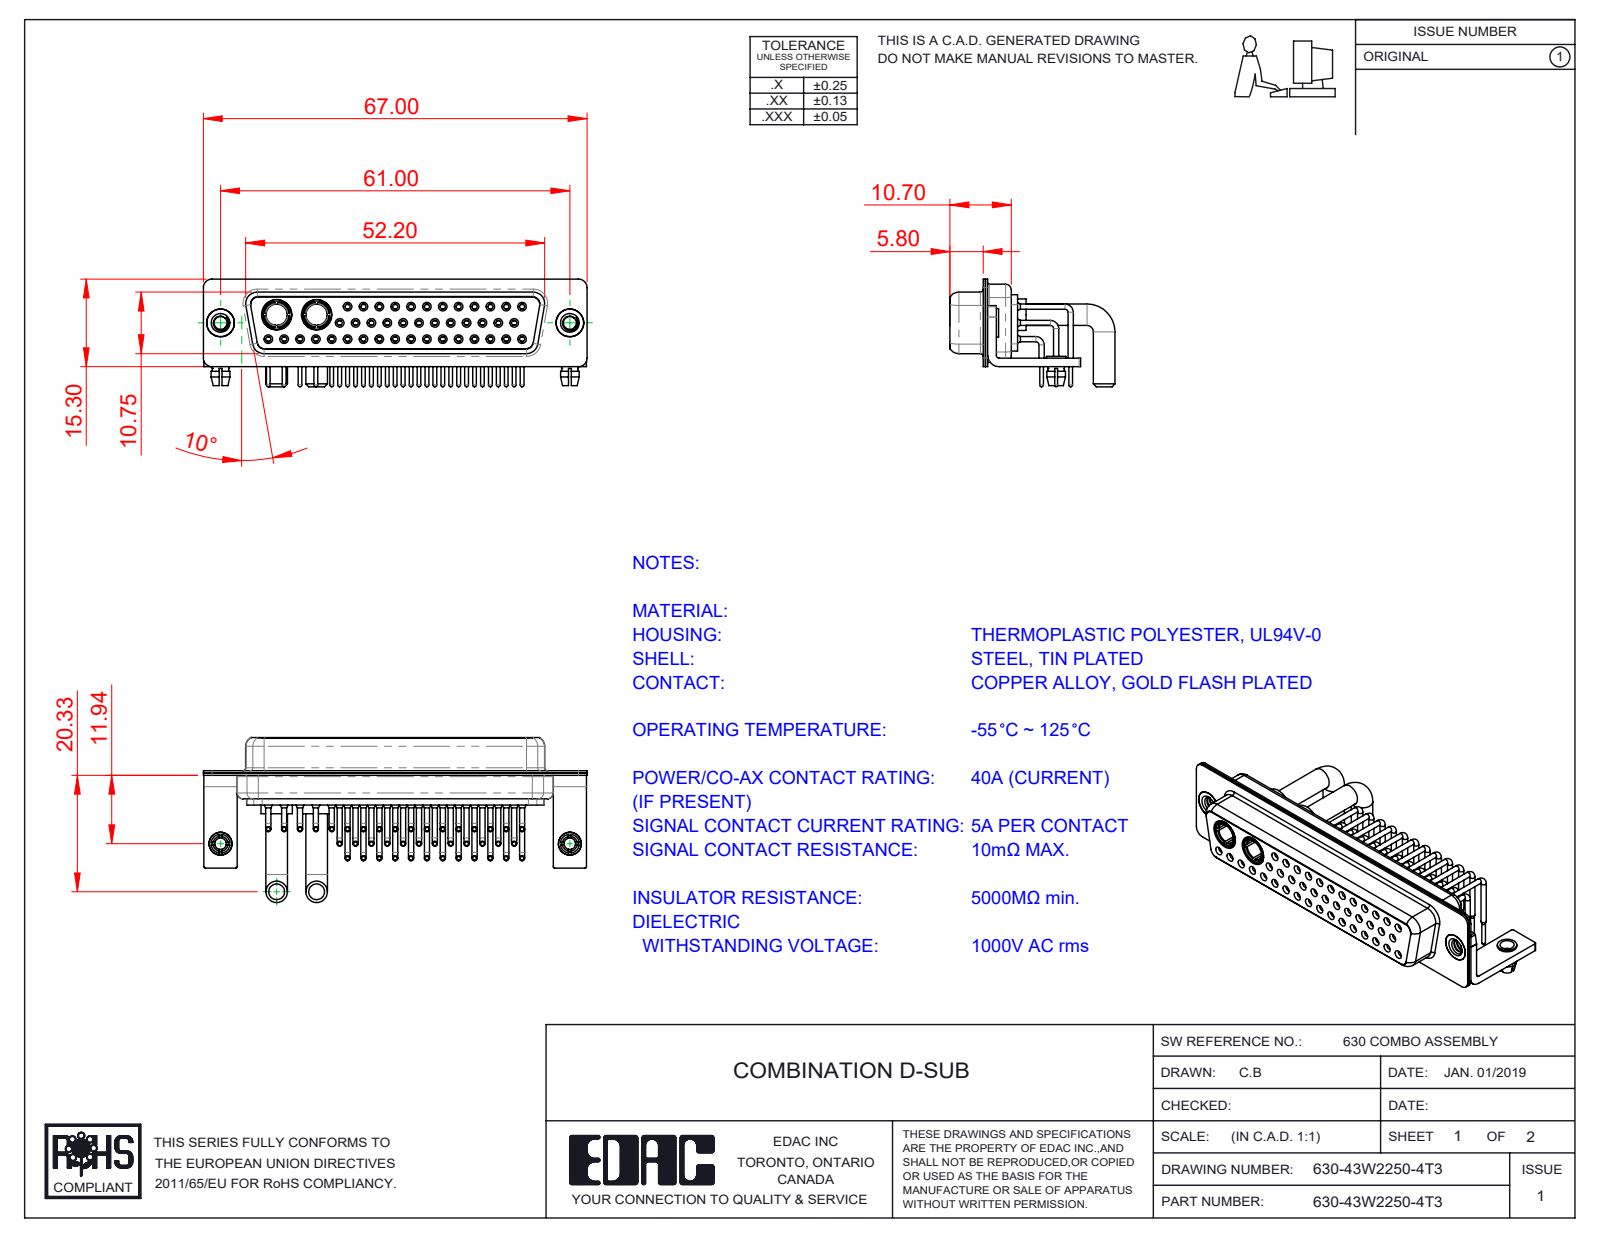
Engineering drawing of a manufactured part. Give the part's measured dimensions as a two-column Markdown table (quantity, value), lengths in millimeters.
| quantity | value |
| --- | --- |
| part name | 630Combo Shell Front_50 Contacts; Power Socket_Ext 40A RA 50; 630Combo Contact Row 2_50 Contacts; 630Combo Contact Row 3 (+7 more) |
| STEP written by | SolidWorks 2020 (CONFIG_CONTROL_DESIGN) |
| units | millimeters |
| bodies | 54 solids, 2740 faces (808 planar, 1180 cylindrical, 752 other) |
| overall size | 67 × 28.8 × 18.8 |
| volume | 7 934 mm³ |
| surface area | 17 047 mm² |
| round holes (diameter × count) | 2 × 43, 0.9 × 41, 1.1 × 41, 1.5 × 41, 1.6 × 29, 1.7 × 12, 4.85 × 4, 2.26 × 2, 2.5 × 2, 3.2 × 2, 3.7 × 2, 4 × 2 |
| round bosses / shafts (diameter × count) | 0.9 × 41, 0.65 × 41, 1.6 × 12, 3.75 × 4, 5.5 × 2, 5.2 × 2, 5 × 2, 4.96 × 2 |
| partial cylindrical surfaces (radius × count) | 0.25 × 16, 1.5 × 16, 2 × 13, 1.35 × 12, 1.6 × 8, 0.5 × 5, 0.6 × 4, 0.65 × 4 |
| main face-to-face distances | 0.4, 1.5, 6, 5.6, 0.8, 5.8, 5.2, 11.28, 1.82, 10.35 |
| hole center spacings | 2.77, 3.16, 5.54, 8.31, 11.08, 13.85, 16.62, 19.39 |
